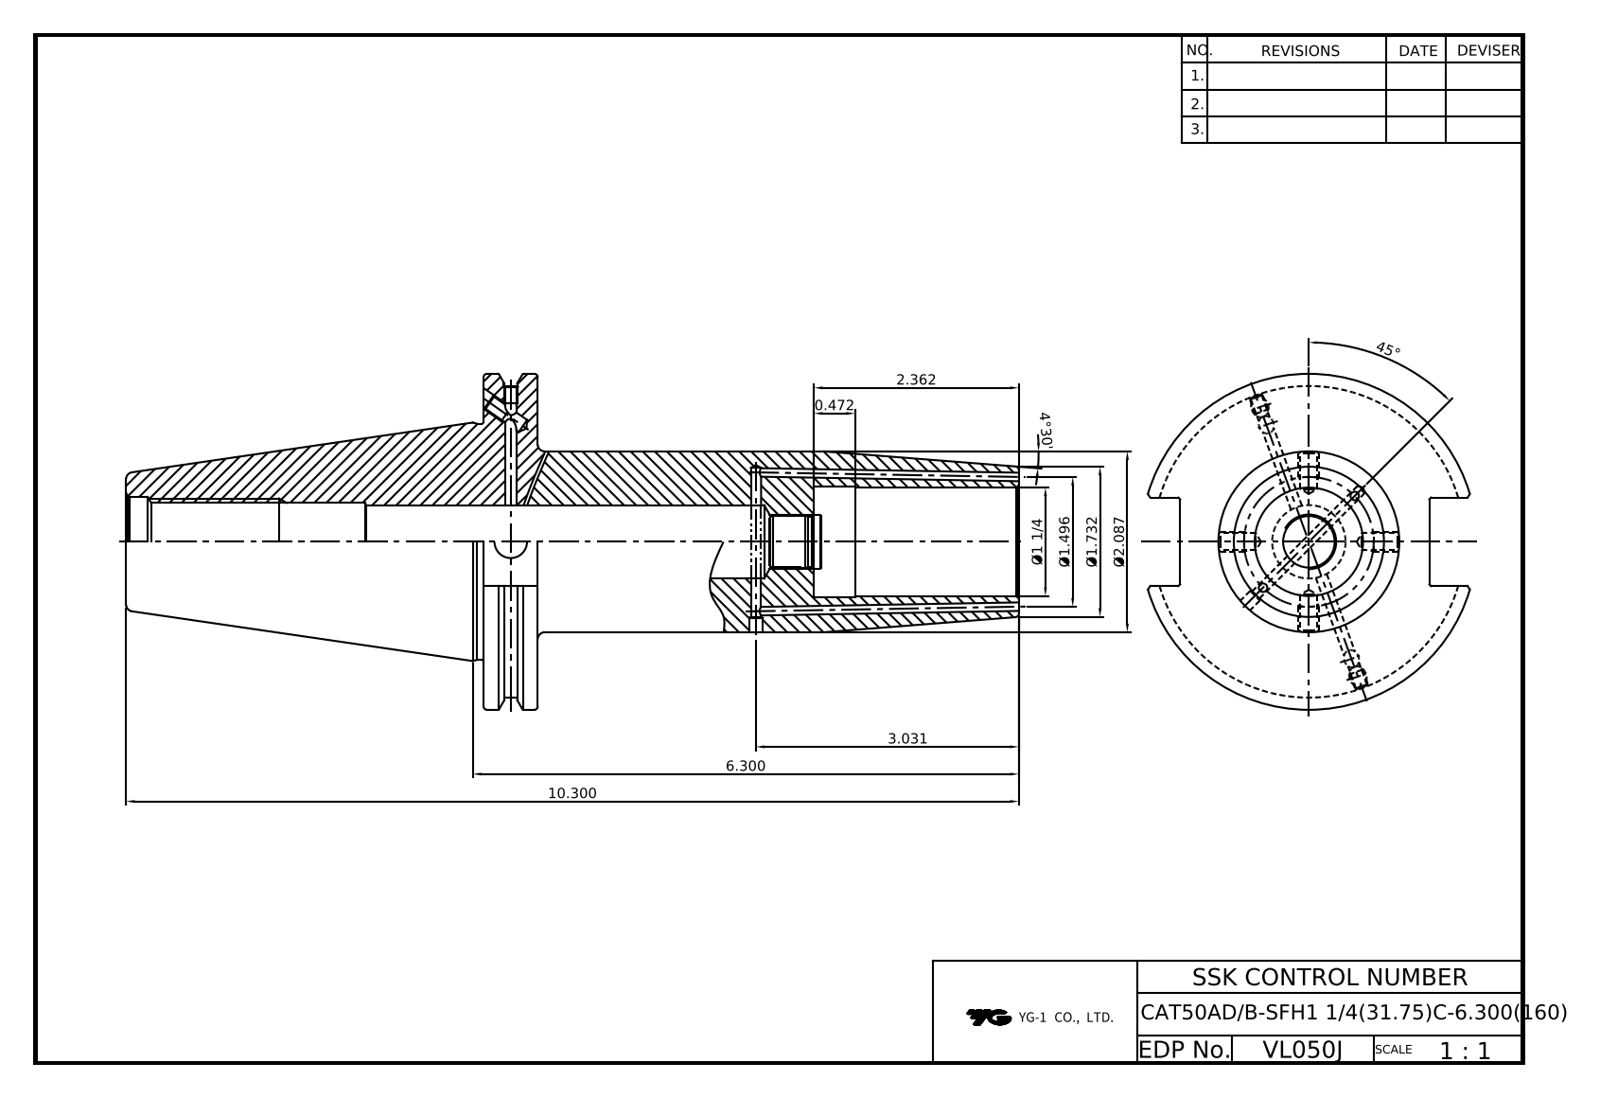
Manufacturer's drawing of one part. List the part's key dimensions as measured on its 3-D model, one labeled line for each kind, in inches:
Part name (STEP PRODUCT): LO-CAT50ADB-SFH31.75C-160
STEP written by: Autodesk Inventor 2025 (AUTOMOTIVE_DESIGN)
Units: inches
Bodies: 1 solid, 88 faces (37 planar, 28 cylindrical, 23 other)
Overall size (bounding box): 10.299 × 3.875 × 3.728
Volume: 32.81 in³ · Surface area: 121.4 in²
Round holes (diameter × count): ⌀0.079 ×2, ⌀0.128 ×2, ⌀0.163 ×2, ⌀0.165 ×2, ⌀0.197 ×2, ⌀0.375 ×1, ⌀0.587 ×1, ⌀0.865 ×1, ⌀1.031 ×1, ⌀1.25 ×1, ⌀1.297 ×1
Round bosses / shafts (diameter × count): ⌀3.875 ×1, ⌀3.594 ×1, ⌀2.726 ×1, ⌀2.087 ×1
Main face-to-face distances: 0.625, 3.812, 3.187, 4.125, 4.75, 7.937, 10.299, 6.174, 5.549, 2.362
